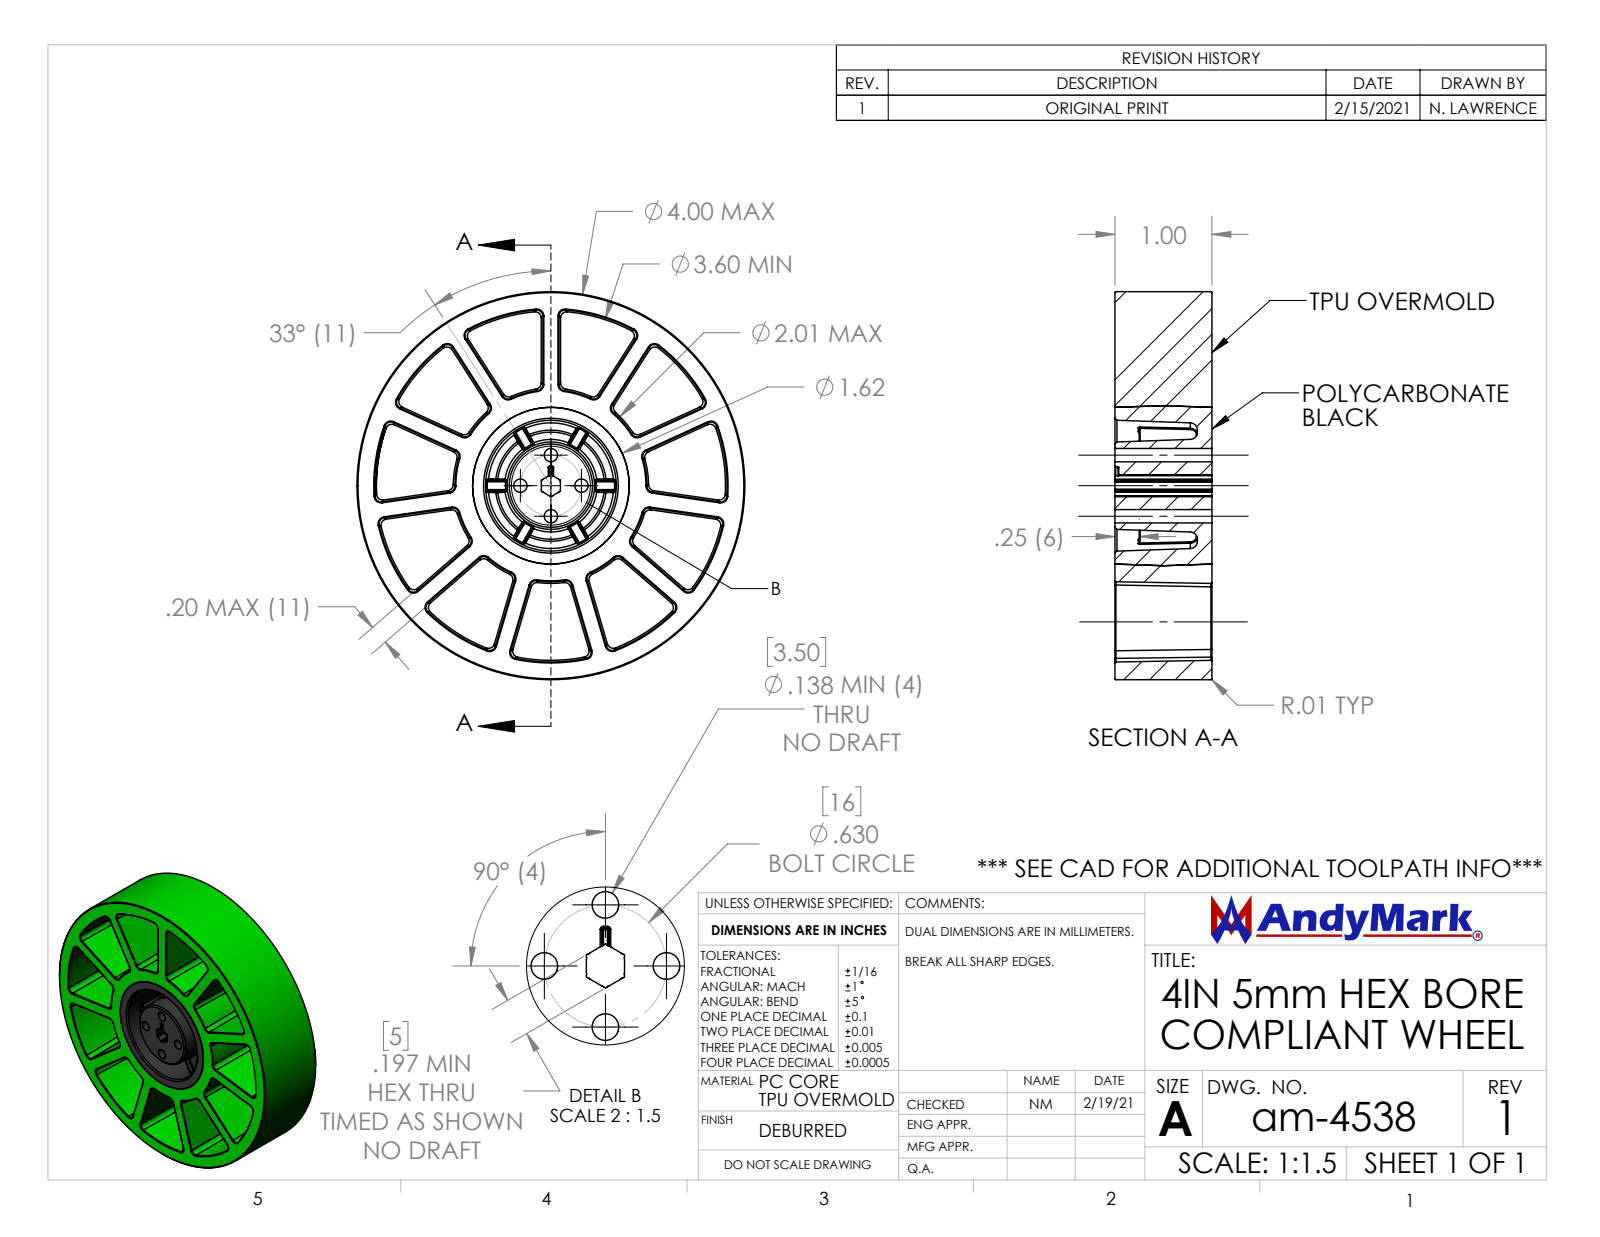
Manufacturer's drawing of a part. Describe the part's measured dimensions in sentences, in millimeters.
The part is named "am-4538 4IN 5mm Hex Compliant Wheel". Its 3-D file was written by "SolidWorks 2019 (AUTOMOTIVE_DESIGN)". It is 2 solids with 474 faces: 73 planar, 93 cylindrical and 308 other. Overall it measures 101.6 by 101.6 by 25.4 millimeters. Its volume is 106 224 cubic millimeters and its surface area 48 533 square millimeters. Round holes: 4 of diameter 3.5. Round bosses or shafts: 1 of diameter 101.6. Partial cylindrical surfaces (rounded edges, fillets, slot ends): 56 of radius 0.25, 20 of radius 0.2. The main face-to-face distances are 25.4, 5, 19.05, 6.35, 3.81, 15.24, 21.59, 24.4, 20.59, 5.35. The hole center spacings are 11.31, 16.
